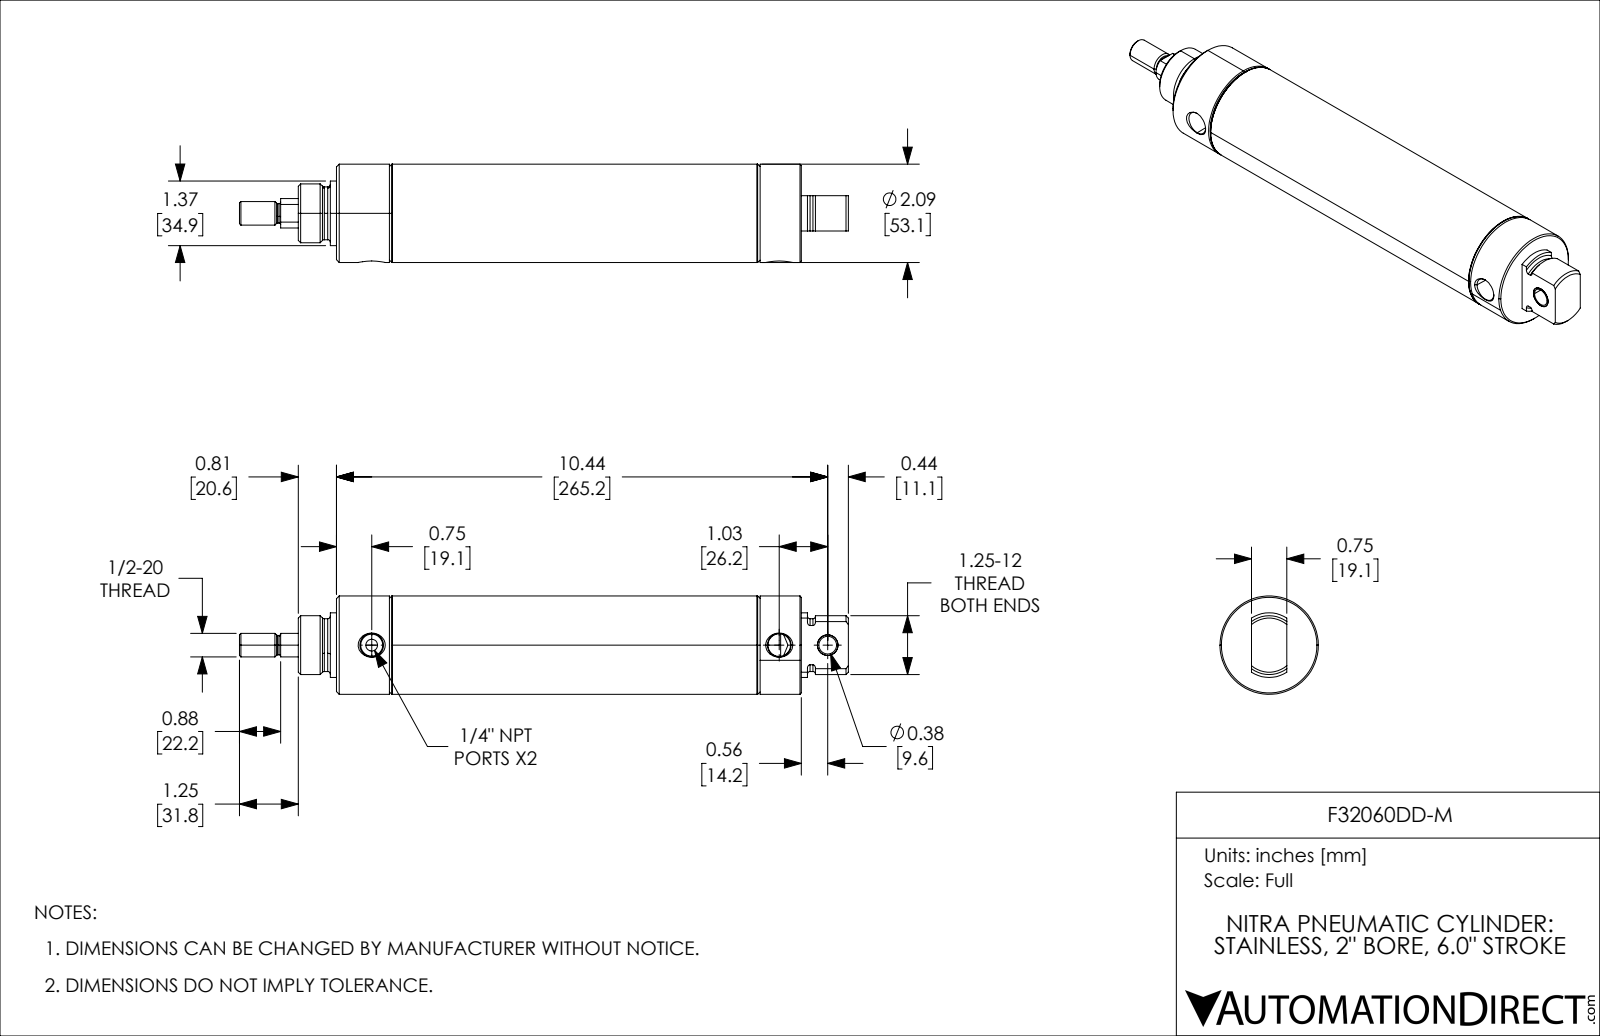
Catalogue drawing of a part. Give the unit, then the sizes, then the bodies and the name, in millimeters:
Units: millimetres
Overall size (bounding box): 328.62 × 53.09 × 53.09
Round holes (diameter × count): ⌀6.35 ×1, ⌀9.55 ×1, ⌀11.15 ×1, ⌀12.18 ×1, ⌀16.52 ×1, ⌀19.05 ×1, ⌀49.05 ×1
Round bosses / shafts (diameter × count): ⌀53.09 ×1, ⌀51.16 ×1, ⌀34.87 ×1, ⌀31.75 ×1, ⌀28.51 ×1, ⌀15.88 ×1, ⌀12.7 ×1, ⌀10.46 ×1
Partial cylindrical surfaces — rounded edges, fillets, slot ends (radius × count): R14.25 ×1
Main face-to-face distances: 30.18, 152.4, 182.58, 212.8, 60.4, 30.22, 38.15, 190.55, 220.73, 250.95
Hole centre spacings: 26.17, 219.96, 246.13
Volume: 290 012 mm³ · Surface area: 119 561 mm²
Bodies: 5 solids, 160 faces (31 planar, 60 cylindrical, 69 other)
Part name (STEP PRODUCT): F32060DD-M; F32060DD-M_9; F32060DD-M_5; F32060DD-M_7 (+2 more)
STEP written by: SolidWorks 2021 (CONFIG_CONTROL_DESIGN)
